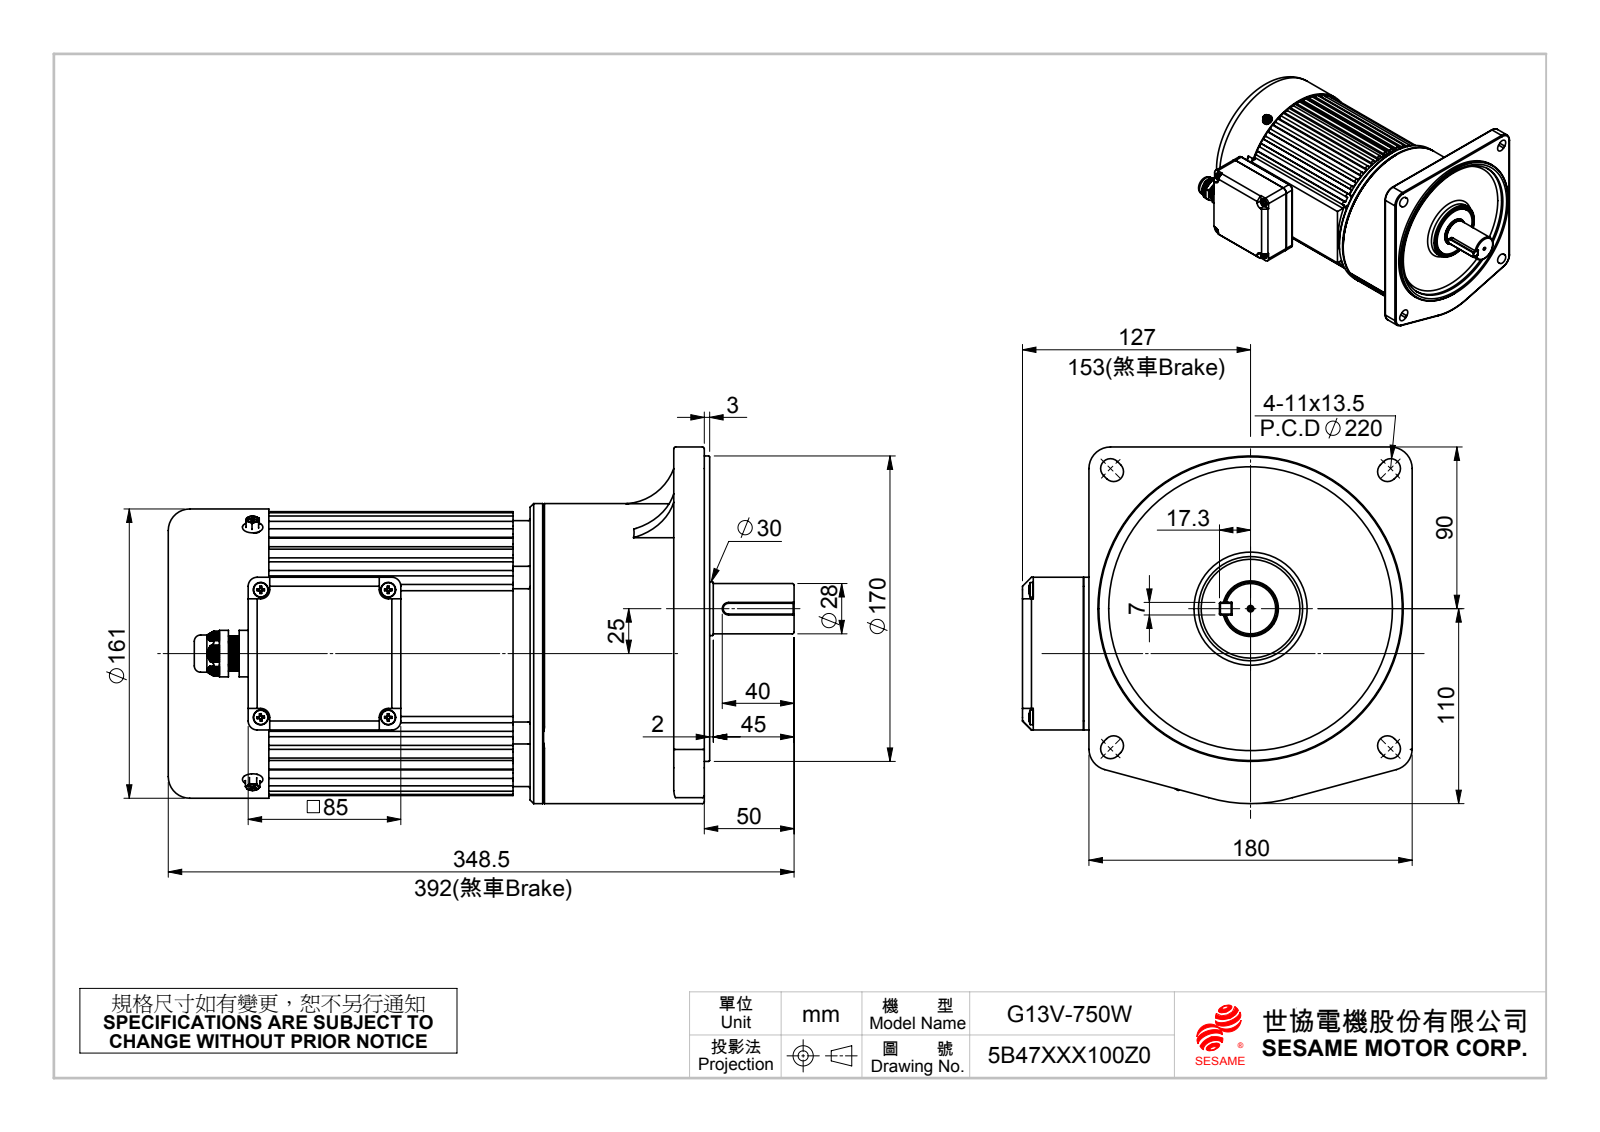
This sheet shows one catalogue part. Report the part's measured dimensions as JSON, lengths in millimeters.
{"part_name": "外六角內十字螺絲M5 x 10_ISO 4162 - M5 x 10 x 10-N; 750後蓋-M-SAB-45_3.烤車鑽; (標準品)G13V750W(5B47XXX100)(減速比共用); 成品-塑膠T盒 (+8 more)", "step_written_by": "SolidWorks 2010 (CONFIG_CONTROL_DESIGN)", "units": "millimeters", "bodies": {"solids": 19, "faces": 2989, "planar": 984, "cylindrical": 934, "other": 1071}, "overall_size": [348.5, 217, 198.5], "volume_mm3": 5892000, "surface_area_mm2": 550233, "round_holes": [[5, 13], [8, 10], [3.3, 9], [4.2, 7], [5.1, 5], [6, 4], [2, 1], [10.8, 1], [16.5, 1], [30, 1], [31, 1], [53, 1]], "round_bosses_or_shafts": [[8.3, 4], [4, 4], [5, 3], [170, 1], [167, 1], [161, 1], [159, 1], [158, 1]], "partial_cylinders_radius": [[1, 46], [2, 46], [3, 16], [5, 8], [5.5, 8], [0.5, 6], [2.5, 6], [8, 5]], "face_to_face_distances": [5, 22, 84.5, 17, 106.5, 157, 9.5, 162, 12, 149.5], "hole_center_spacings": [144.57, 45, 64.77, 66, 71, 89.35, 76, 108.92]}
